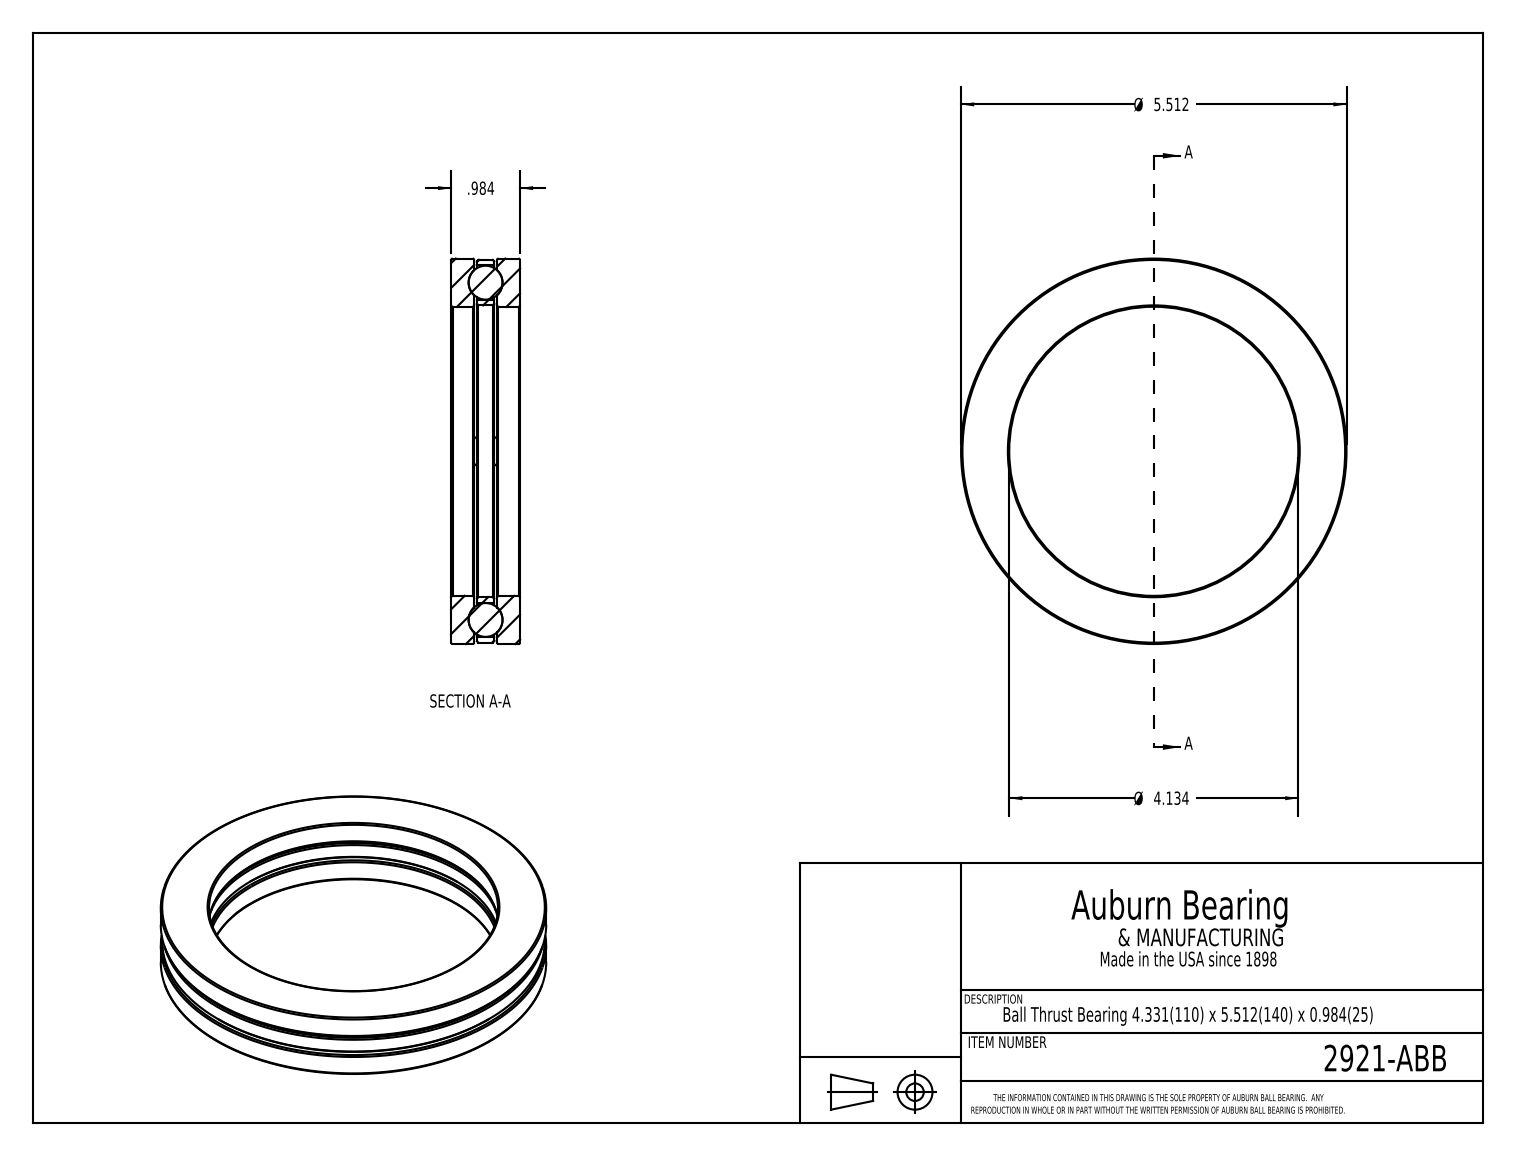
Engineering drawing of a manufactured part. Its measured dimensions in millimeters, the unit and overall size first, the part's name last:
Units: millimetres
Overall size (bounding box): 140 × 140 × 25
Round holes (diameter × count): ⌀12.5 ×4, ⌀110 ×1, ⌀111 ×1
Round bosses / shafts (diameter × count): ⌀140 ×1, ⌀139 ×1
Main face-to-face distances: 9.4, 15.6, 25, 6.2, 8.3, 16.7, 1, 7.3, 8.3
Hole centre spacings: 62.5, 88.4, 125
Volume: 123 100 mm³ · Surface area: 54 160 mm²
Bodies: 7 solids, 36 faces (8 planar, 10 cylindrical, 18 other)
Part name (STEP PRODUCT): 2921-ABB
STEP written by: SolidWorks 2017 (CONFIG_CONTROL_DESIGN)
